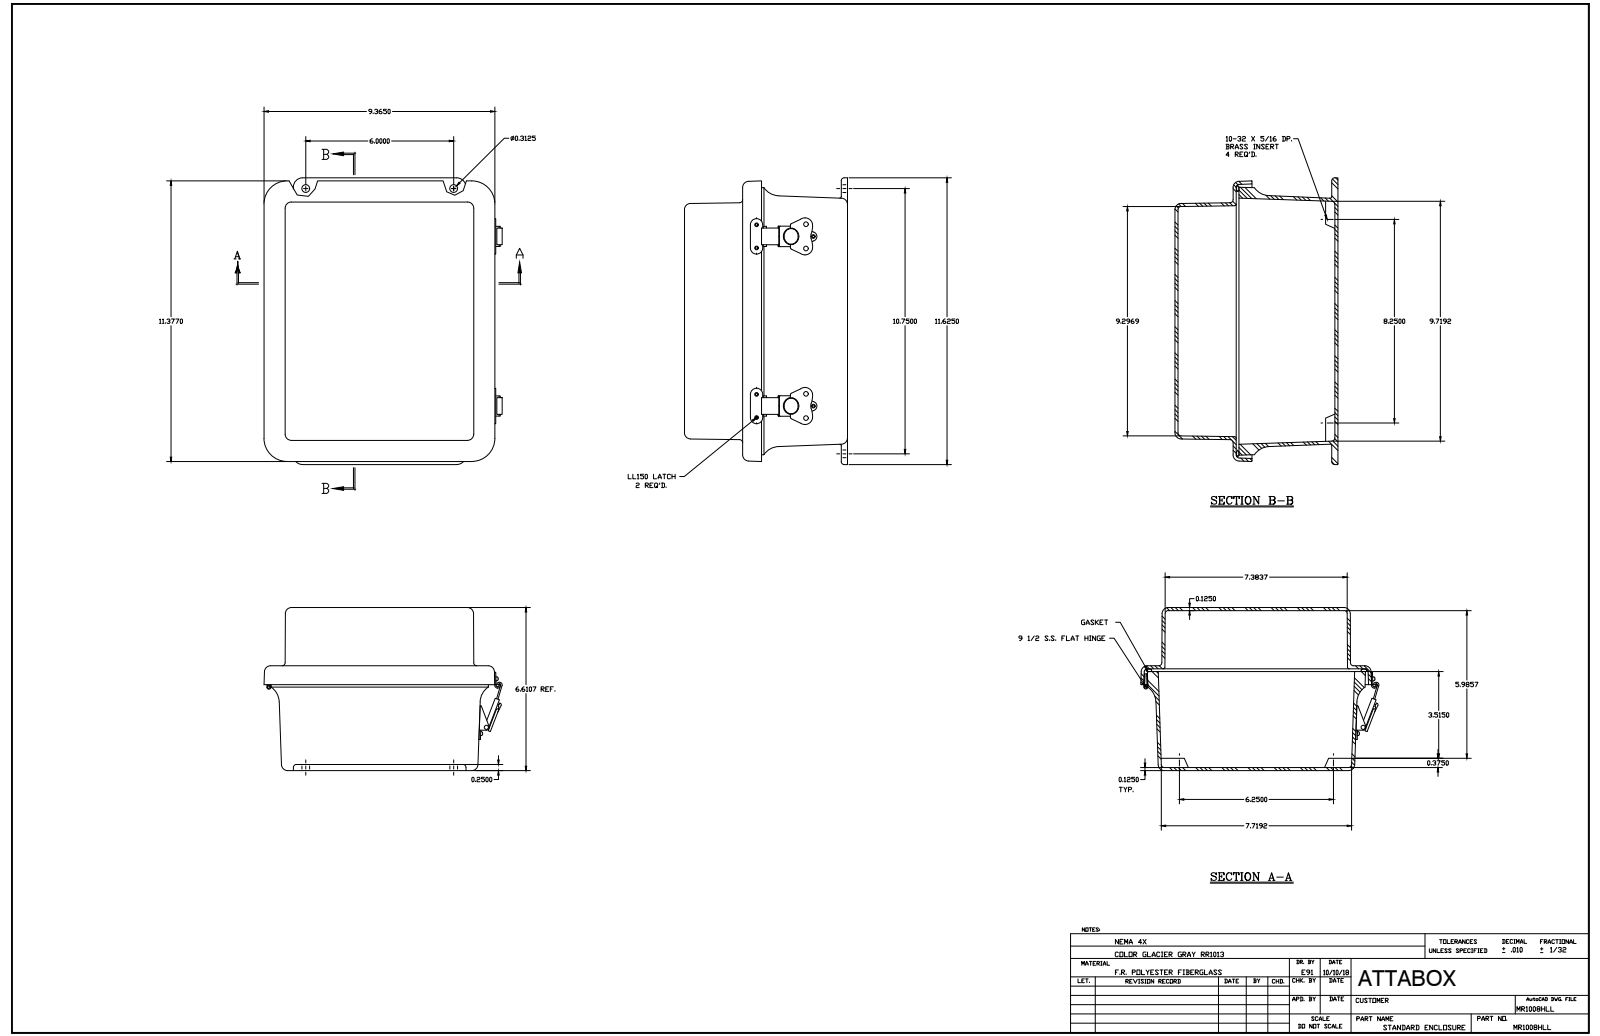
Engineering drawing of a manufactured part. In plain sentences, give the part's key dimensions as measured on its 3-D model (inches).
The part is named "MR1008HLL". Its 3-D file was written by "SolidWorks 2018 (AUTOMOTIVE_DESIGN)". It is 48 solids with 1151 faces: 495 planar, 441 cylindrical and 215 other. Overall it measures 11.625 by 9.593 by 6.594 inches. Its volume is 69.04 cubic inches and its surface area 984 square inches. Round holes: 16 of diameter 0.14, 8 of diameter 0.131, 5 of diameter 0.152, 4 of diameter 0.13, 4 of diameter 0.156, 4 of diameter 0.165, 4 of diameter 0.197, 4 of diameter 0.218, 2 of diameter 0.118, 2 of diameter 0.138, 2 of diameter 0.181, 2 of diameter 0.182. Round bosses or shafts: 16 of diameter 0.25, 10 of diameter 0.125, 6 of diameter 0.125, 4 of diameter 0.27, 2 of diameter 0.583, 2 of diameter 0.524, 2 of diameter 0.209, 2 of diameter 0.185. Partial cylindrical surfaces (rounded edges, fillets, slot ends): 24 of radius 0.125, 20 of radius 0.031, 20 of radius 0.079, 12 of radius 0.25, 8 of radius 0.037, 8 of radius 0.039, 8 of radius 0.045, 8 of radius 0.047. The main face-to-face distances are 0.125, 0.125, 6.344, 6.469, 6.594, 6.469, 4.109, 3.984, 2.36, 2.485. The hole center spacings are 7, 6, 3, 0.25, 0.701, 0.826, 0.938, 1.337.
